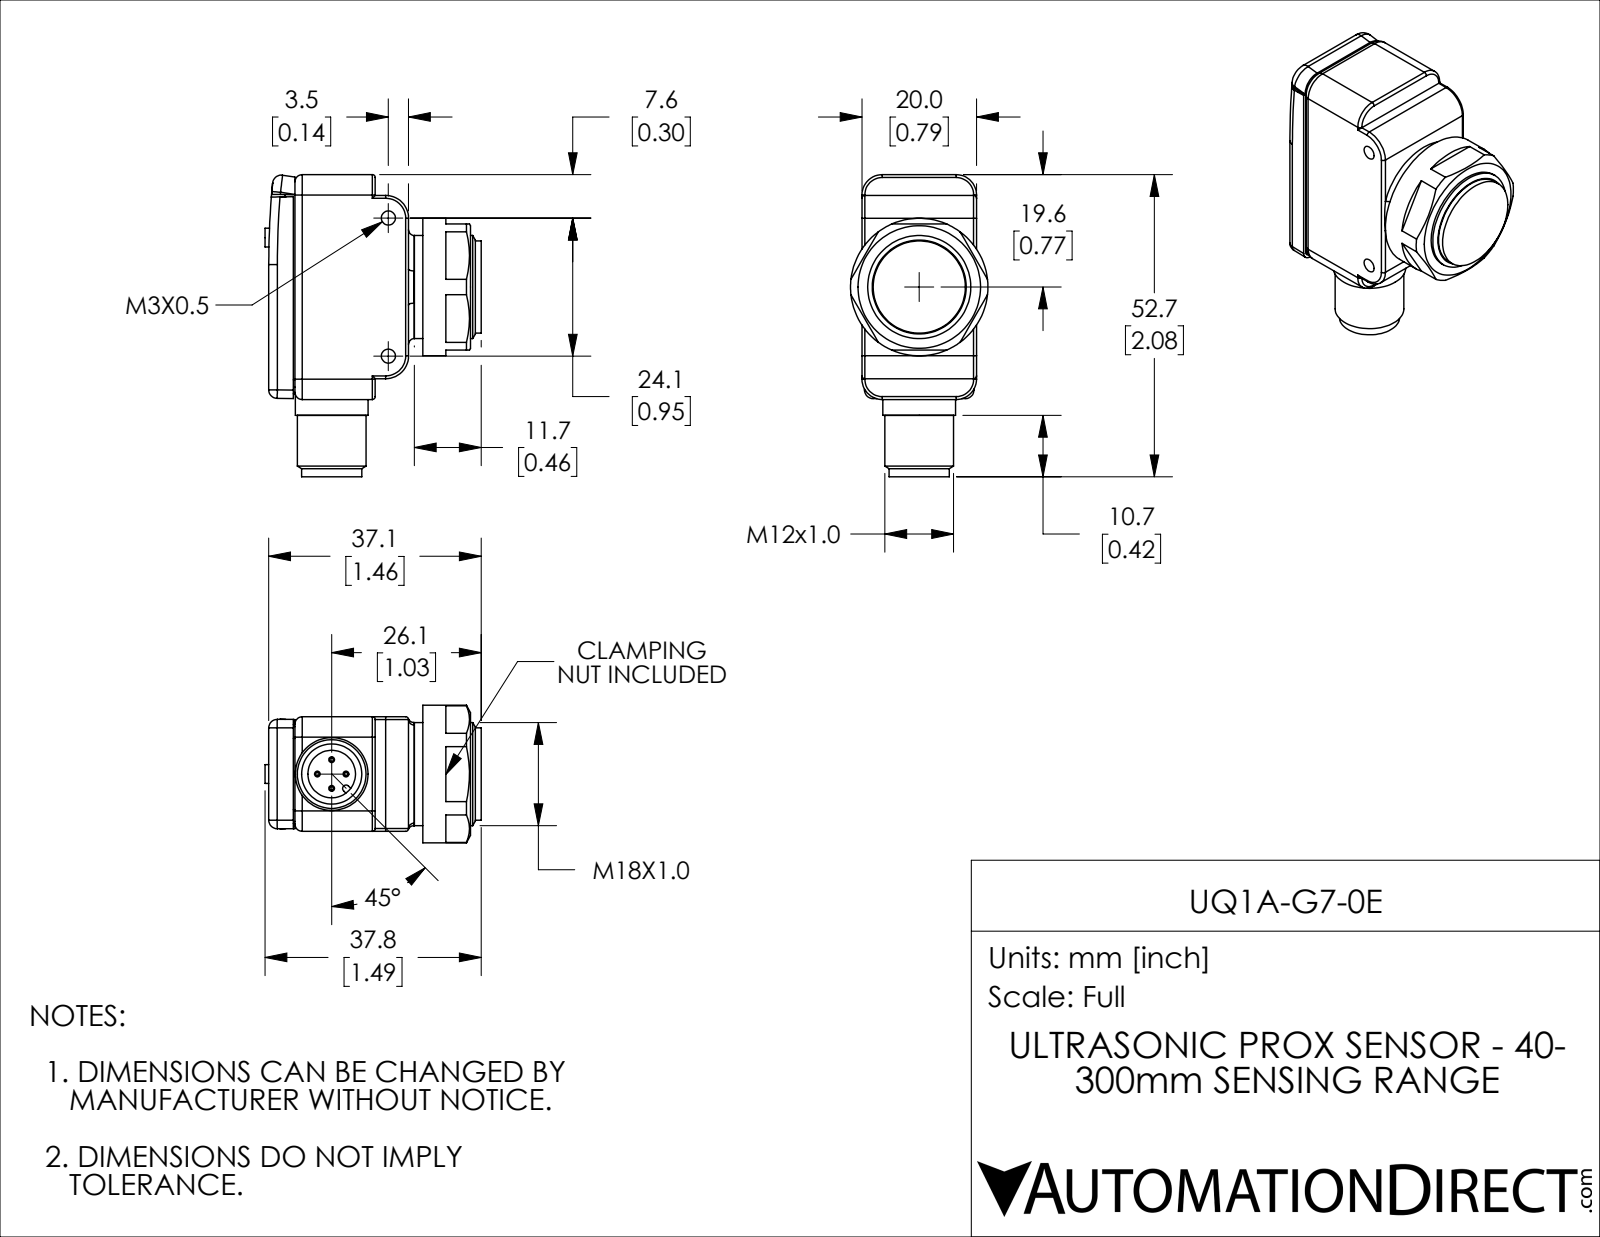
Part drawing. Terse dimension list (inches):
name: UQ1A-G7-0E
written by: SolidWorks 2018 (AUTOMOTIVE_DESIGN)
unit: in
bodies: 7 solids, 203 faces (81 planar, 72 cylindrical, 50 other)
size: 2.076 × 1.486 × 0.945
volume: 1.389 in³; area: 17.13 in²
holes: 2× ⌀0.097, 1× ⌀0.13, 1× ⌀0.327
bosses: 4× ⌀0.039, 1× ⌀0.945, 1× ⌀0.709, 1× ⌀0.634, 1× ⌀0.5, 1× ⌀0.472, 1× ⌀0.413
rounds: 10× R0.02, 6× R0.059, 4× R0.049, 4× R0.14, 2× R0.118, 2× R0.157, 2× R5.906, 1× R0.024
face distances: 0.091, 0.787, 0.911, 0.82, 0.09, 0.181, 1.001, 0.459, 1.46, 1.37
hole spacings: 0.949
